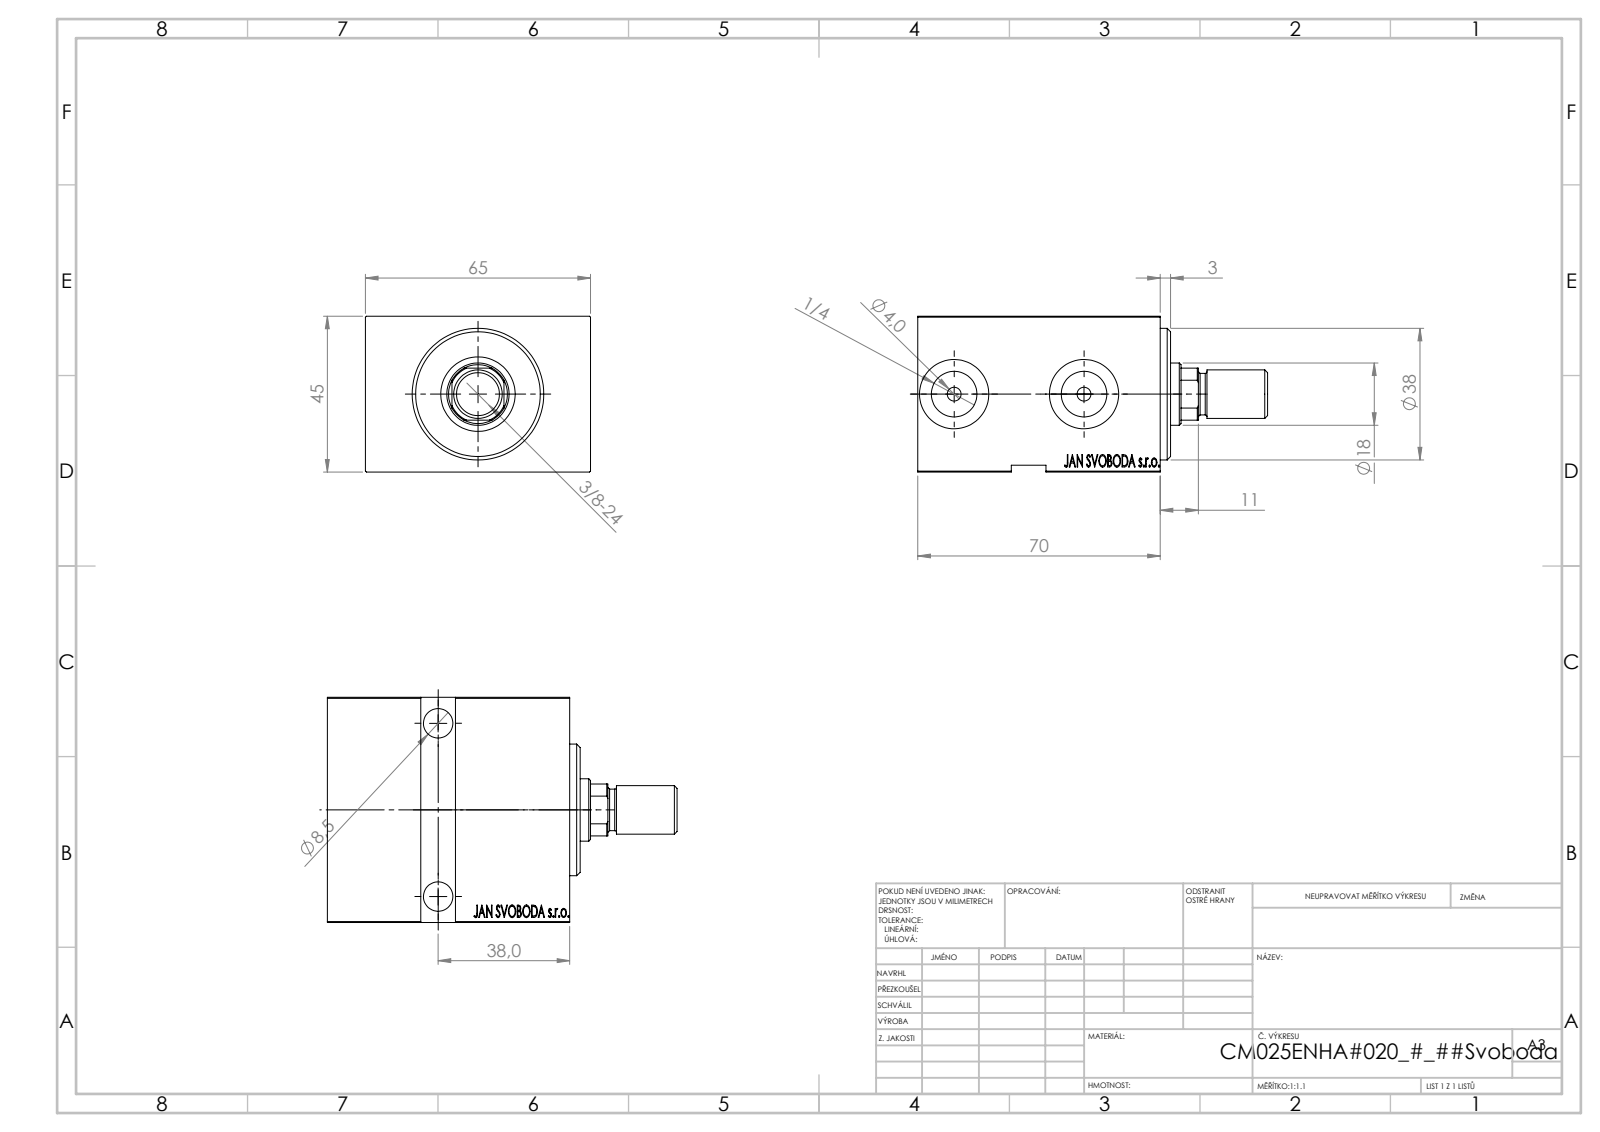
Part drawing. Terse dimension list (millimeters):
name: V450CM_MALE_METRIC; V450CM_VC_B; V450CM_E_VCP; V450CM_E_Body
written by: SolidWorks 2019 (CONFIG_CONTROL_DESIGN)
unit: mm
bodies: 4 solids, 859 faces (411 planar, 48 cylindrical, 400 other)
size: 101 × 65 × 45
volume: 197 175 mm³; area: 42 543 mm²
holes: 3× ⌀8.5, 2× ⌀4, 2× ⌀13.16, 2× ⌀13.5, 2× ⌀20, 1× ⌀18, 1× ⌀21.5, 1× ⌀25, 1× ⌀35
bosses: 1× ⌀38, 1× ⌀27, 1× ⌀14, 1× ⌀12
rounds: 1× R8.5
face distances: 45, 65, 70, 64, 6, 8, 5, 59, 3, 43
hole spacings: 37.5, 50
